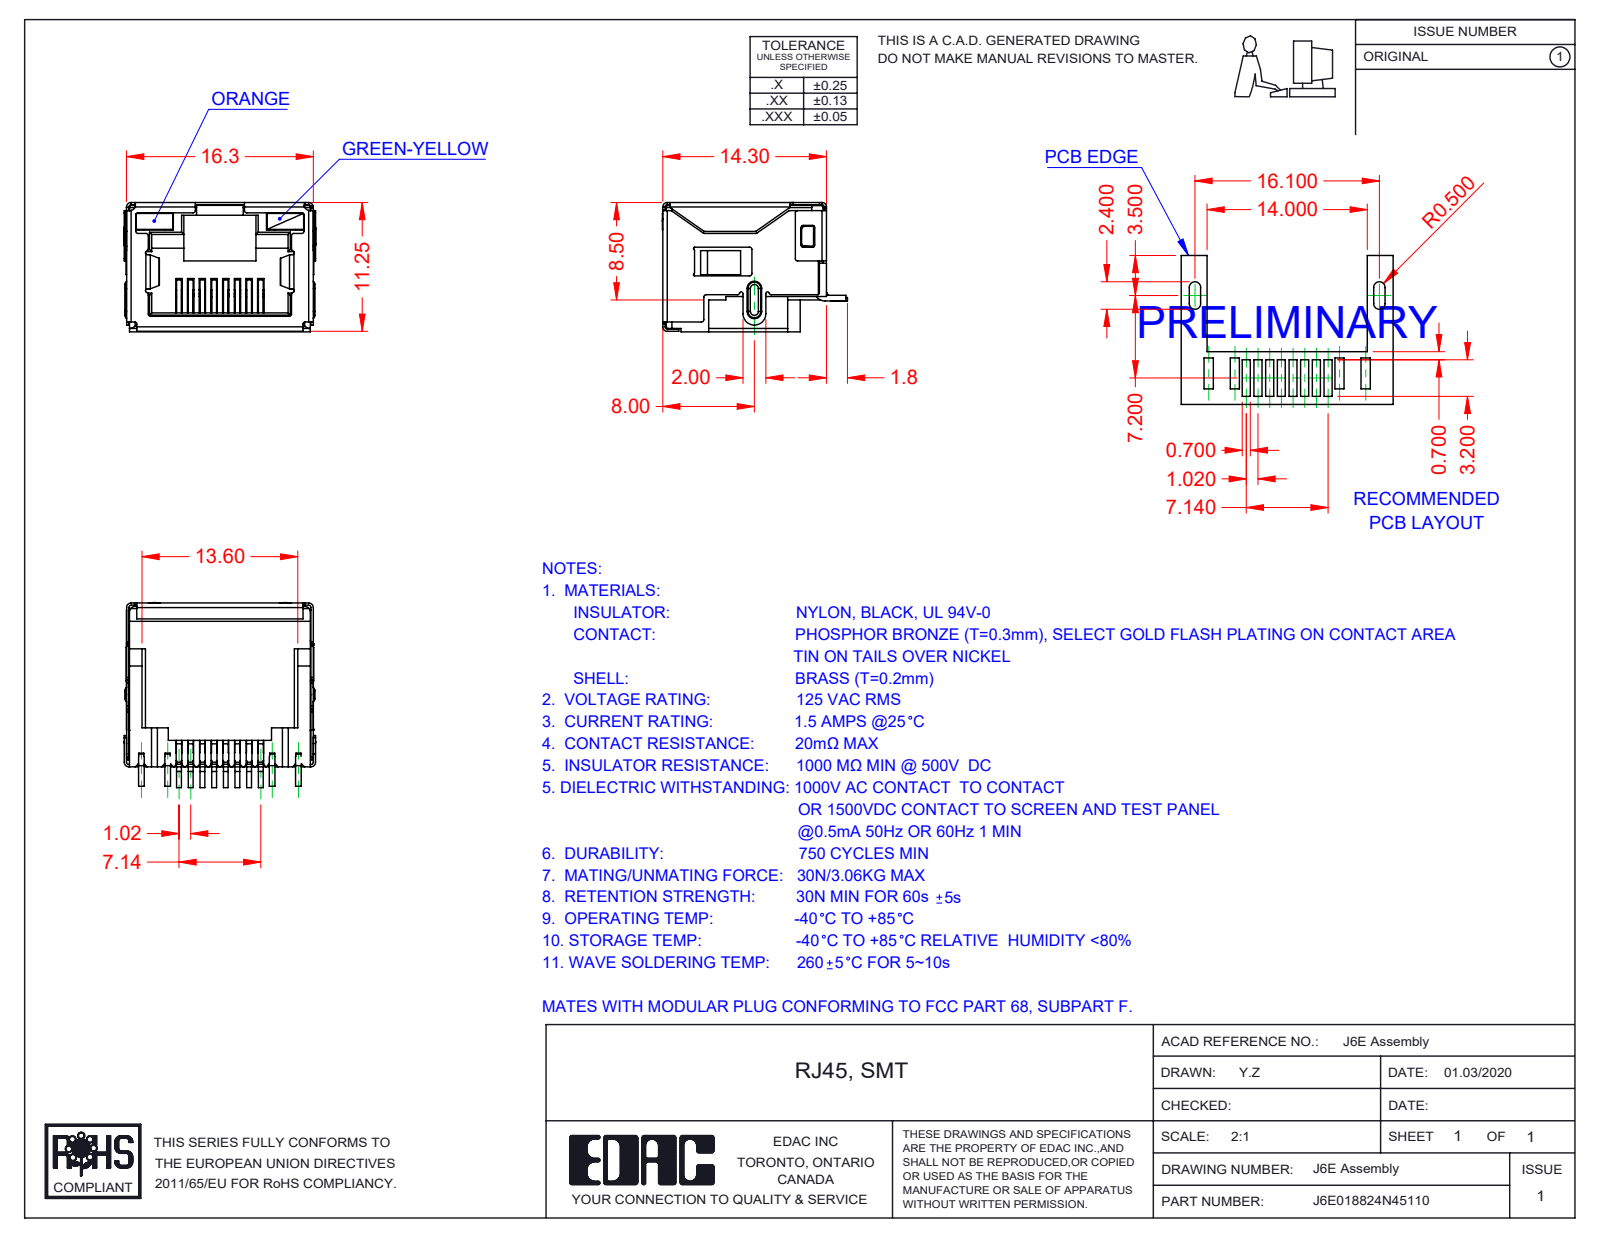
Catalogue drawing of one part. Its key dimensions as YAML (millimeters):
part_name: "6E Contacts; 6E LED LH_4-Orange; 6E Shield_LED; J6E018824N45110 (+2 more)"
step_written_by: "SolidWorks 2016 (CONFIG_CONTROL_DESIGN)"
units: millimeters
bodies: {solids: 12, faces: 1498, planar: 1099, cylindrical: 349, other: 50}
overall_size: [16.75, 16.15, 11.3]
volume: 1109
surface_area: 4045
partial_cylinders:
  - {radius: 0.2, count: 82}
  - {radius: 0.25, count: 17}
  - {radius: 0.4, count: 13}
  - {radius: 0.5, count: 13}
  - {radius: 0.1, count: 10}
  - {radius: 0.15, count: 7}
  - {radius: 0.3, count: 4}
  - {radius: 1, count: 3}
face_to_face_distances: [11.05, 16.05, 16.1, 15.85, 11.1, 11.3, 2.4, 0.7, 9.85, 0.49]
